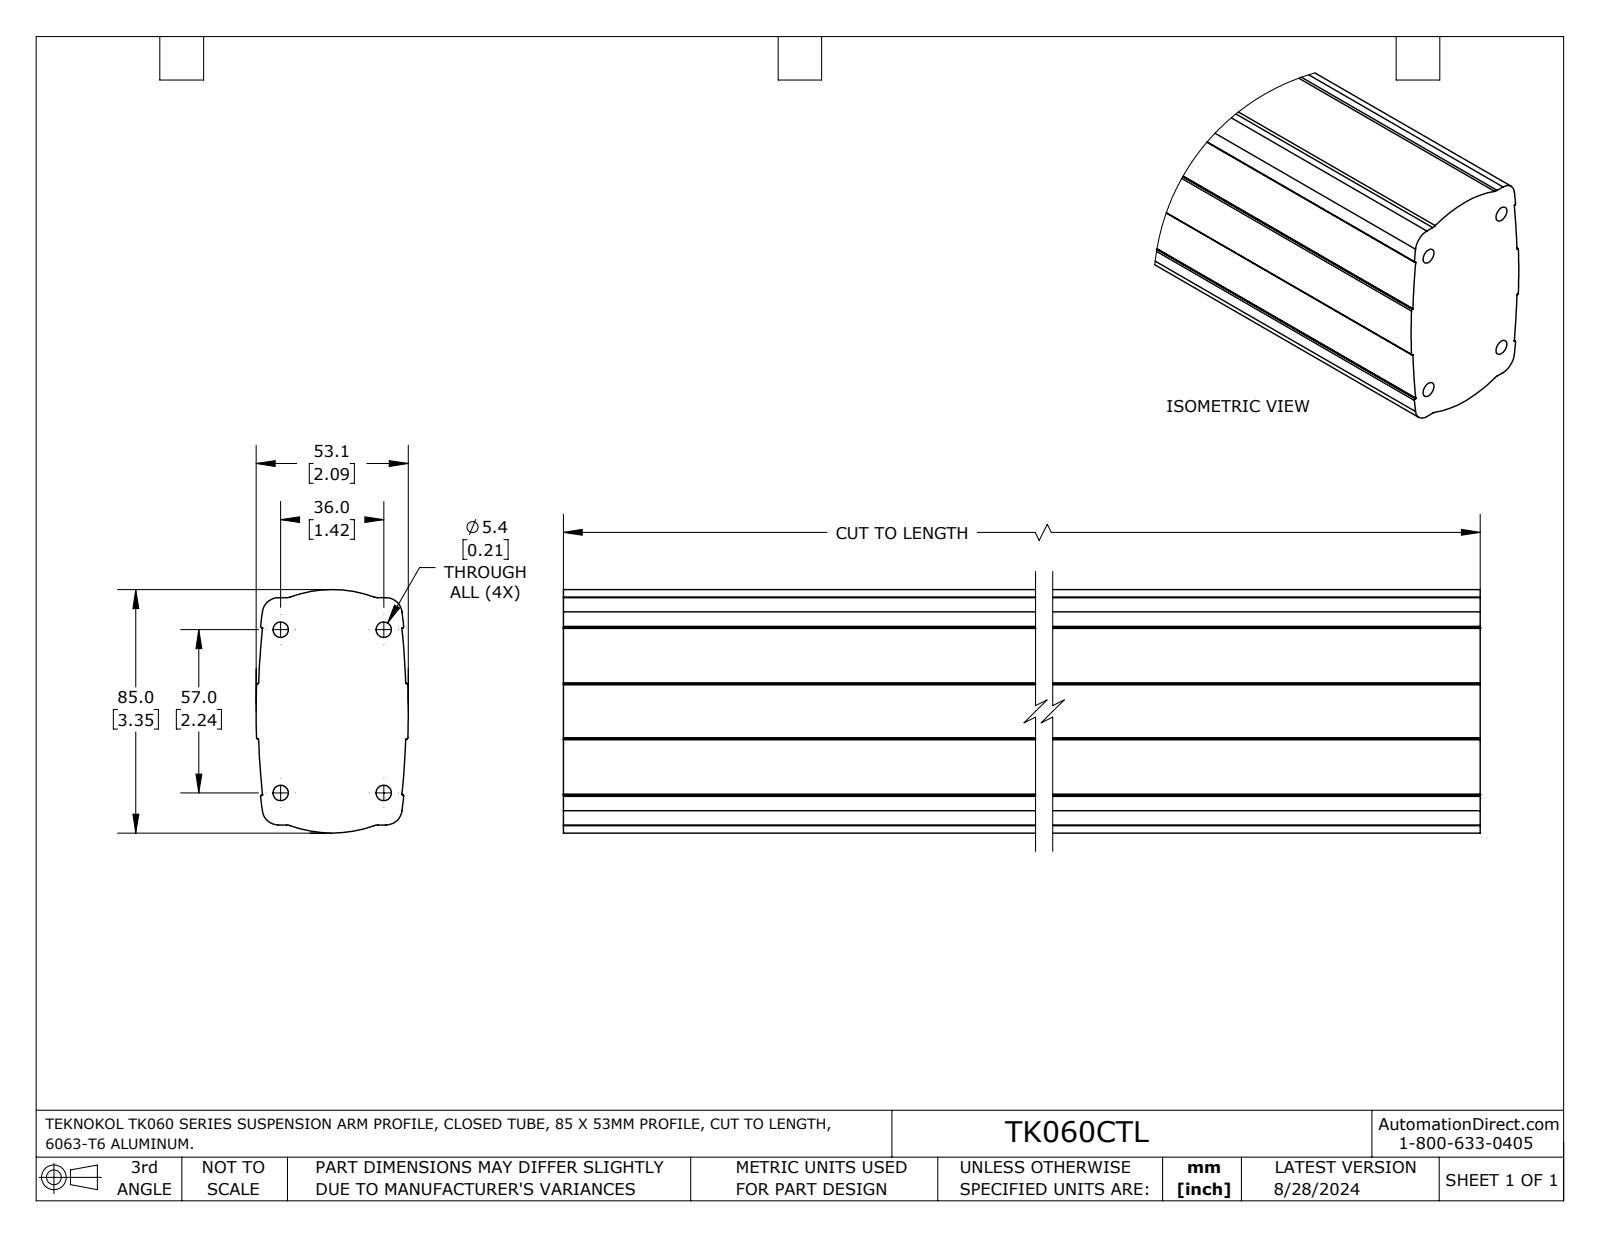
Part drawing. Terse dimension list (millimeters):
name: TK060.200
written by: SolidWorks 2023 (AUTOMOTIVE_DESIGN)
unit: mm
bodies: 1 solid, 54 faces (14 planar, 40 cylindrical, 0 other)
size: 2000 × 85 × 53.1
volume: 8 028 000 mm³; area: 647 100 mm²
holes: 4× ⌀5.4
rounds: 8× R0.2, 8× R0.5, 4× R3.5, 4× R5.7, 2× R278.4, 2× R279.1, 1× R42.5
face distances: 79.3, 2000, 52.8, 17.6
hole spacings: 36, 57, 67.4
